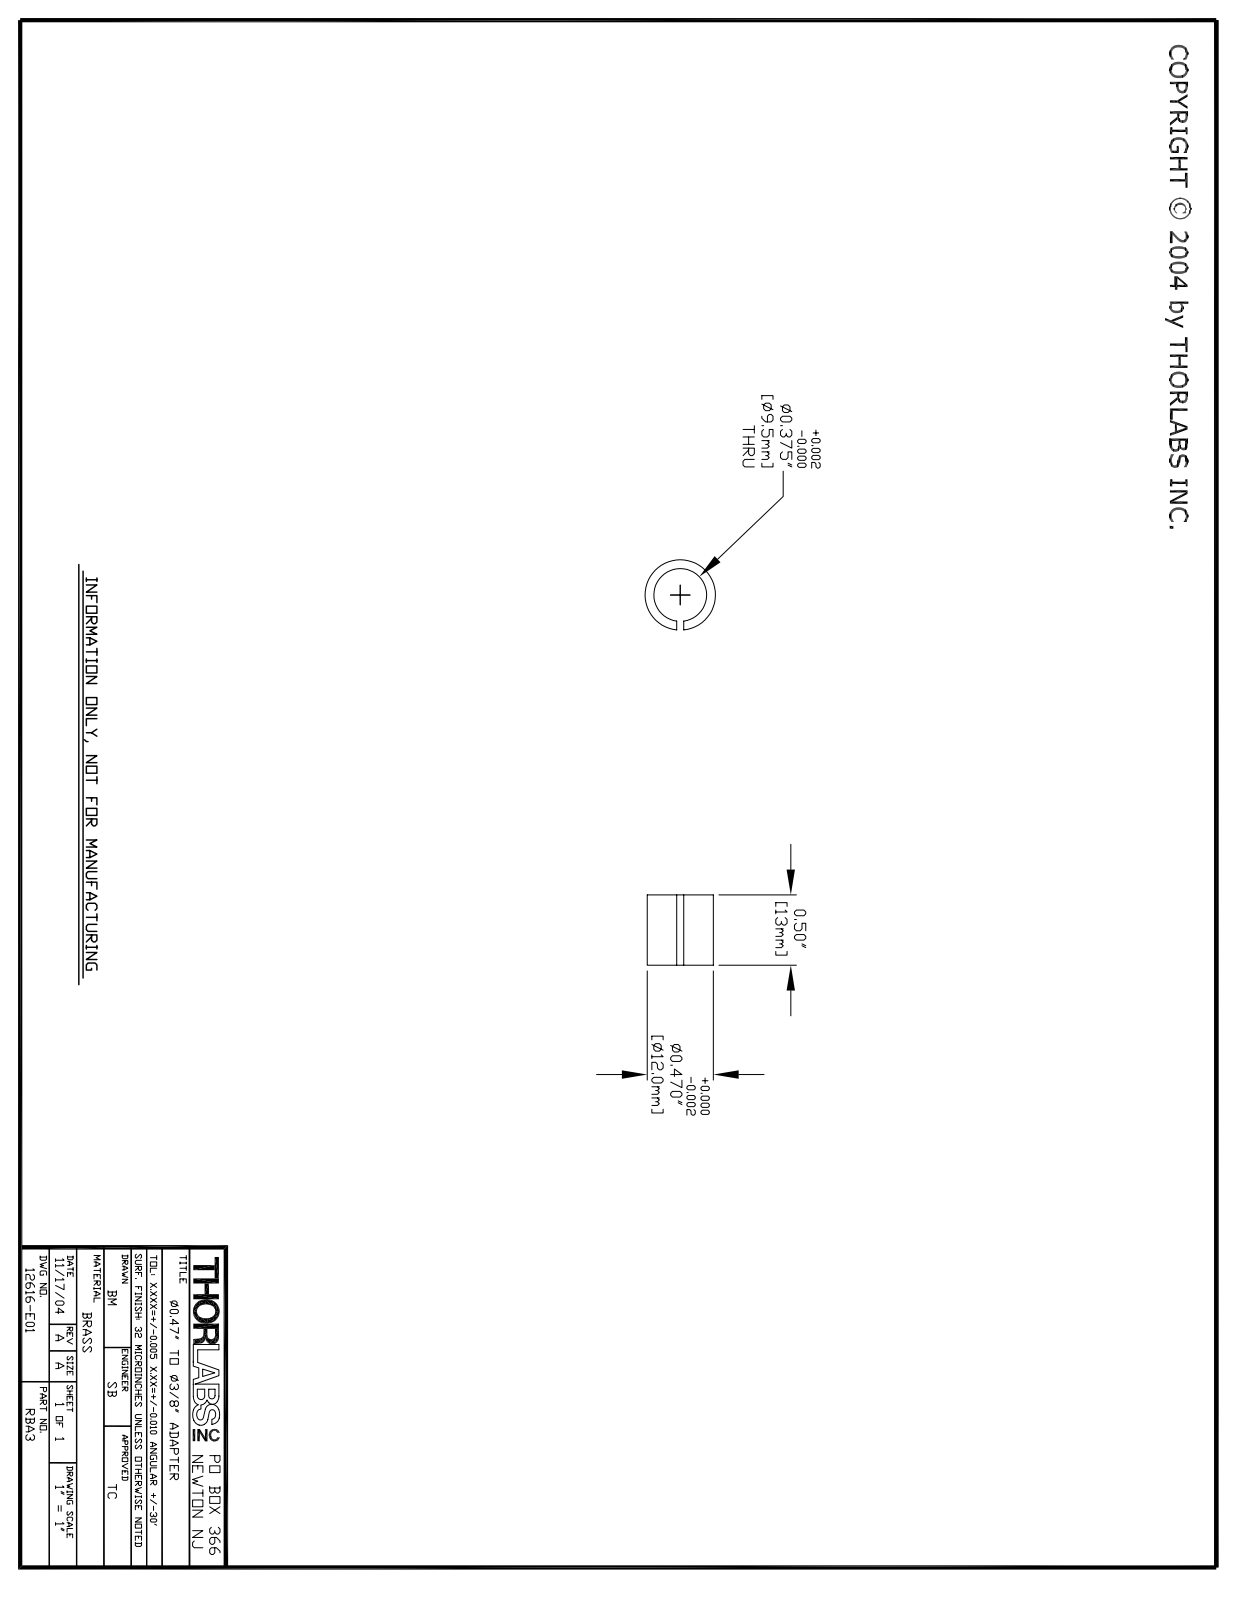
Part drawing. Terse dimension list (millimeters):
name: 12616-E0W
written by: SolidWorks 2011 (CONFIG_CONTROL_DESIGN)
unit: mm
bodies: 1 solid, 10 faces (4 planar, 6 cylindrical, 0 other)
size: 12.7 × 11.9 × 11.9
volume: 490 mm³; area: 933 mm²
holes: 1× ⌀9.6
bosses: 1× ⌀11.9
face distances: 12.7, 1.3
